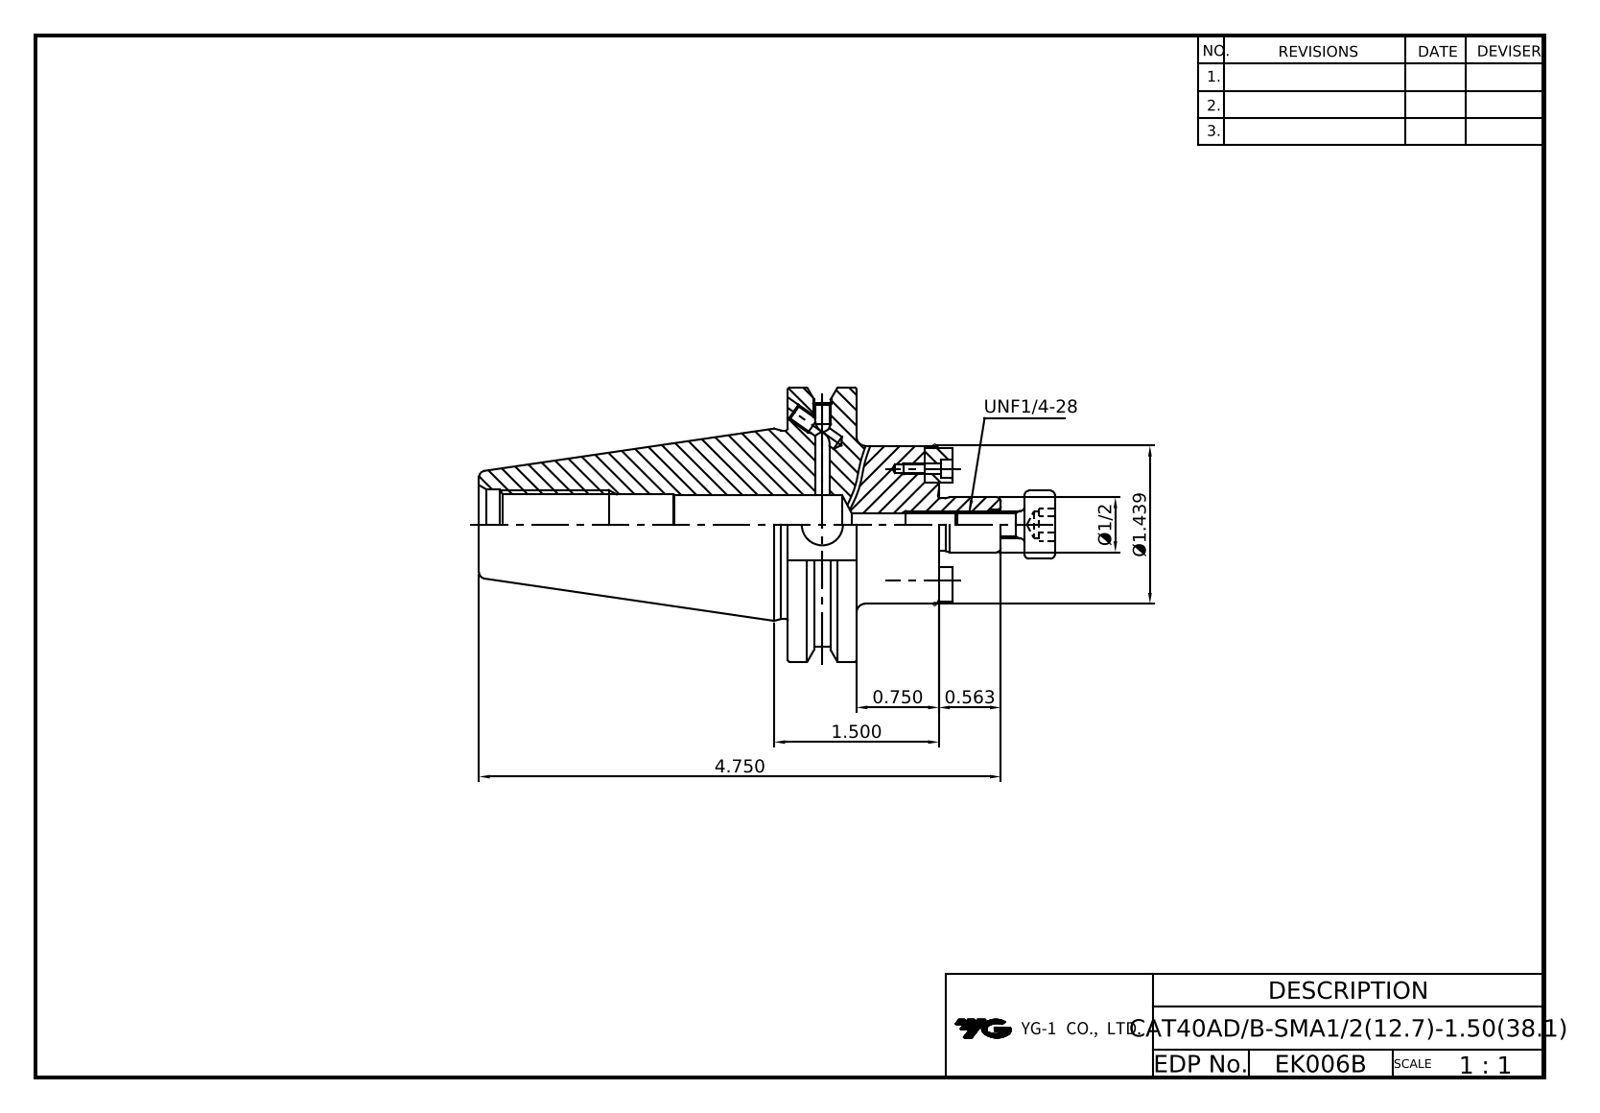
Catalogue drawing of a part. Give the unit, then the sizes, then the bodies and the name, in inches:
Units: inches
Overall size (bounding box): 5.338 × 2.5 × 2.405
Round holes (diameter × count): ⌀0.128 ×4, ⌀0.165 ×4, ⌀0.076 ×2, ⌀0.102 ×2, ⌀0.157 ×2, ⌀0.211 ×1, ⌀0.25 ×1, ⌀0.276 ×1, ⌀0.375 ×1, ⌀0.512 ×1, ⌀0.527 ×1, ⌀0.642 ×1
Round bosses / shafts (diameter × count): ⌀0.161 ×2, ⌀0.099 ×2, ⌀2.5 ×1, ⌀1.717 ×1, ⌀1.438 ×1, ⌀0.618 ×1, ⌀0.5 ×1
Partial cylindrical surfaces — rounded edges, fillets, slot ends (radius × count): R0.125 ×2, R1.108 ×1
Main face-to-face distances: 0.625, 1.375, 0.75, 0.126, 1.249, 0.624, 1.874, 0.645, 2.812, 3.437
Hole centre spacings: 0.47, 0.94
Volume: 7.563 in³ · Surface area: 40.41 in²
Bodies: 6 solids, 171 faces (88 planar, 46 cylindrical, 37 other)
Part name (STEP PRODUCT): LO-CAT40ADB-SMA12.7-38; CAT40ADB-SMA12.7-38.1; HEX'' WRENCH BOLT-UNC#3-48x1_4L; DRIVE KEY-6.35x6.35x8 (+1 more)
STEP written by: Autodesk Inventor 2022 (AUTOMOTIVE_DESIGN)
